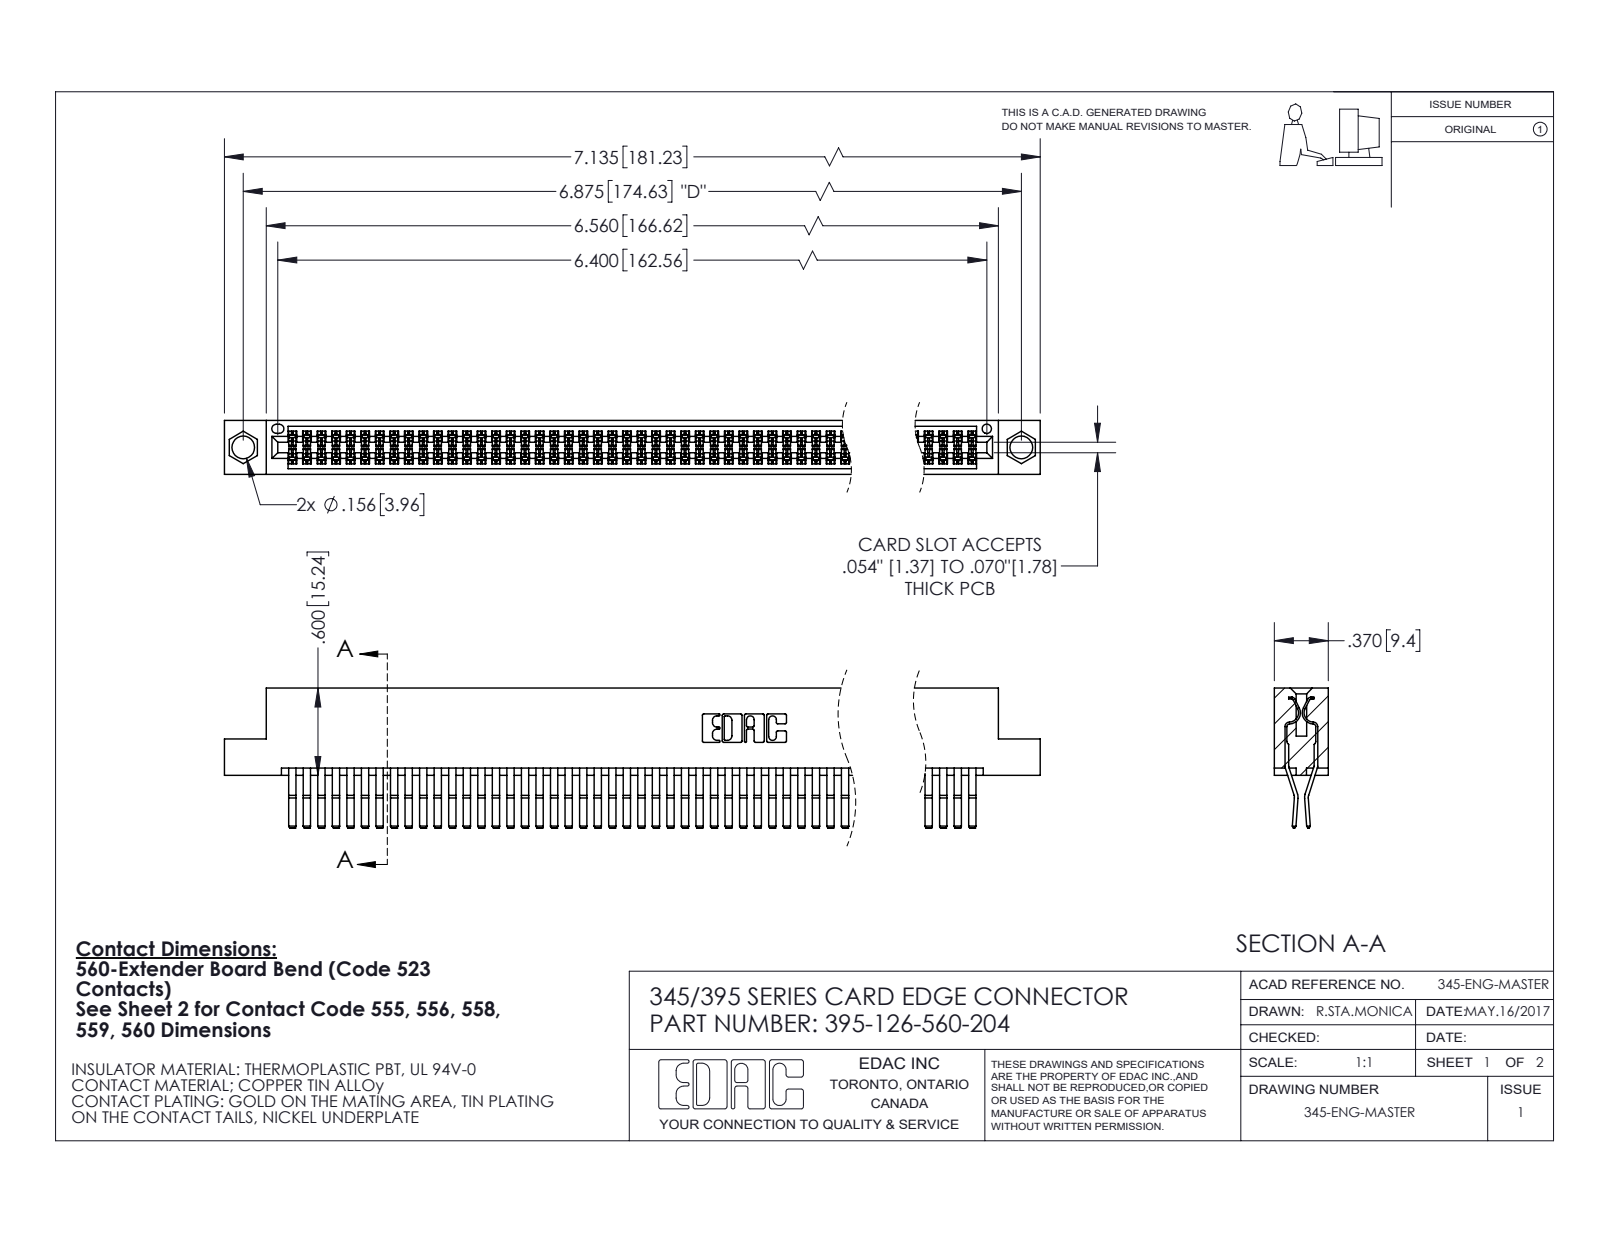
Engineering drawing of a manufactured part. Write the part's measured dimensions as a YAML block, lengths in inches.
part_name: "395-126-560-204; 345-292-001_560 Tail; 345 Part_Flush Mounting Lugs - 0.156 Dia-TI"
step_written_by: "SolidWorks 2020 (CONFIG_CONTROL_DESIGN)"
units: inches
bodies: {solids: 127, faces: 6692, planar: 4252, cylindrical: 2440, other: 0}
overall_size: [7.135, 0.962, 0.37]
volume: 1.13
surface_area: 46.12
round_holes:
  - {diameter: 0.156, count: 2}
  - {diameter: 0.064, count: 1}
partial_cylinders:
  - {radius: 0.006, count: 189}
  - {radius: 0.01, count: 22}
  - {radius: 0.007, count: 6}
  - {radius: 0.031, count: 6}
  - {radius: 0.026, count: 3}
  - {radius: 0.01, count: 2}
  - {radius: 0.014, count: 2}
  - {radius: 0.019, count: 2}
face_to_face_distances: [0.025, 0.298, 0.072, 0.37, 0.2, 0.098, 0.272, 0.225, 0.175, 0.149]
hole_center_spacings: [0.27, 6.639, 6.875]
